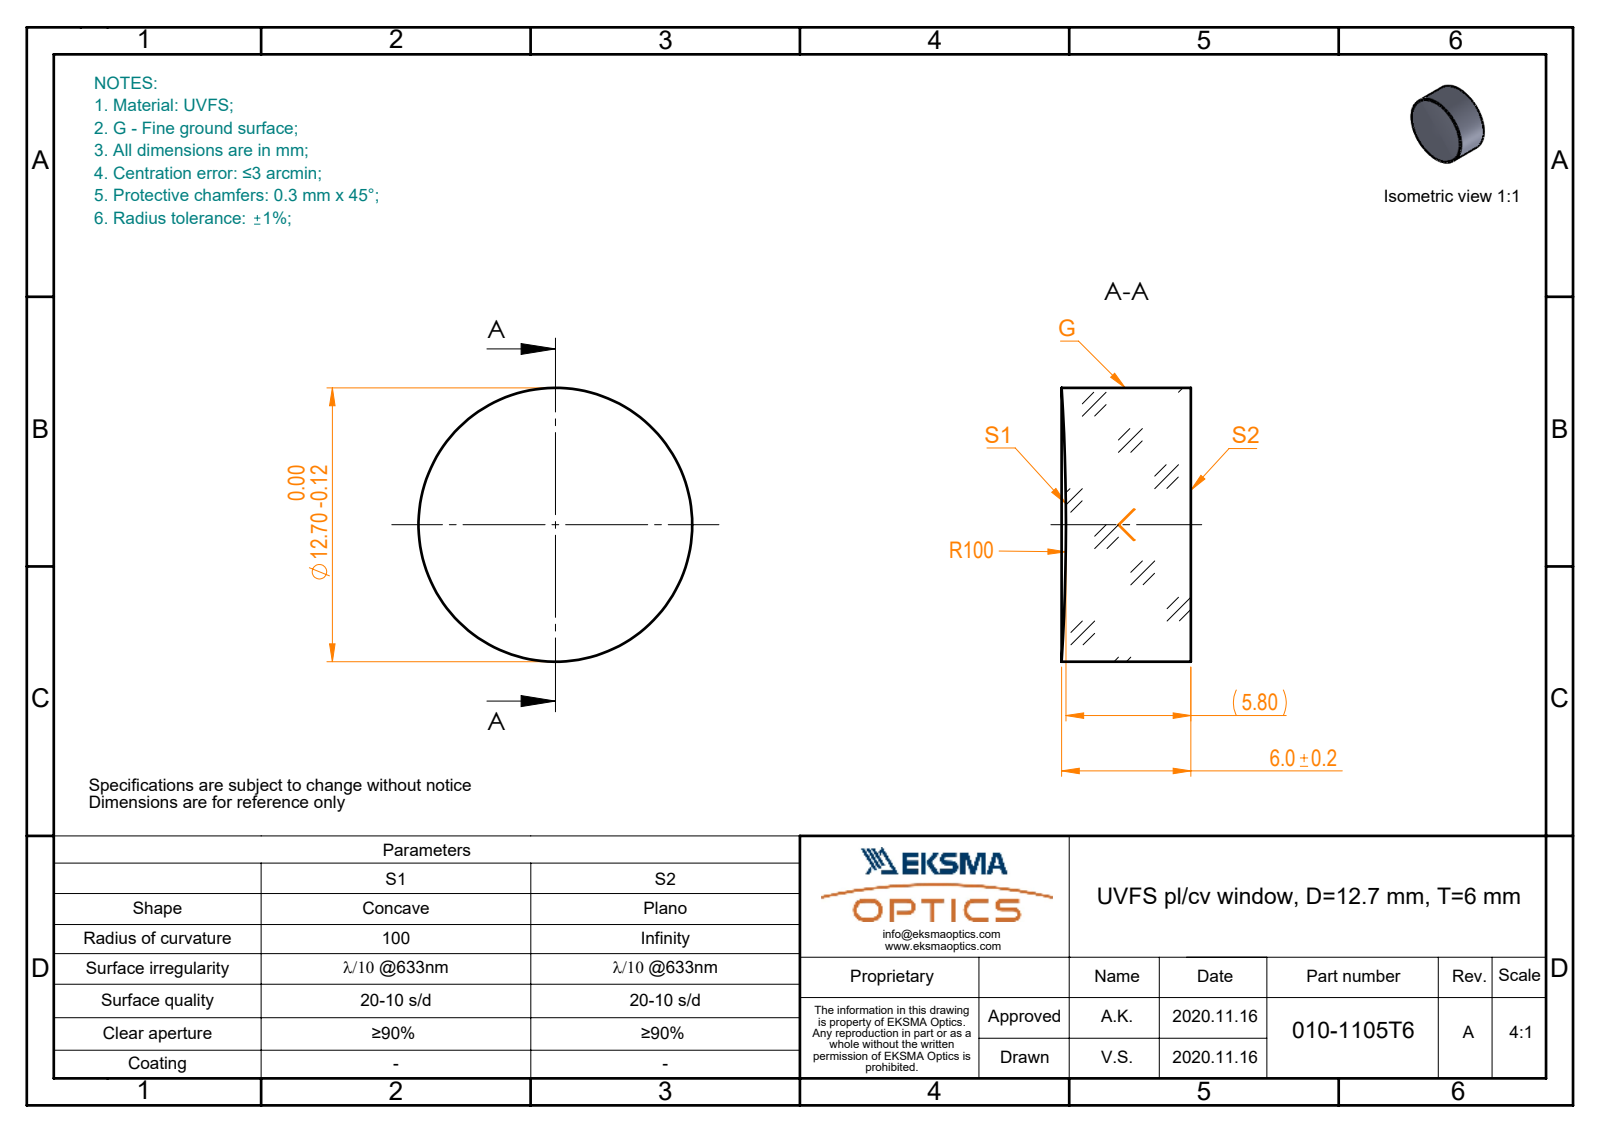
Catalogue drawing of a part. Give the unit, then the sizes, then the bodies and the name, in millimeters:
Units: millimetres
Overall size (bounding box): 12.7 × 12.7 × 6
Round bosses / shafts (diameter × count): ⌀12.7 ×1
Volume: 747 mm³ · Surface area: 493 mm²
Bodies: 1 solid, 5 faces (1 planar, 2 cylindrical, 2 other)
Part name (STEP PRODUCT): 010-1105T6_UVFS_PCV_window
STEP written by: SolidWorks 2019 (CONFIG_CONTROL_DESIGN)
